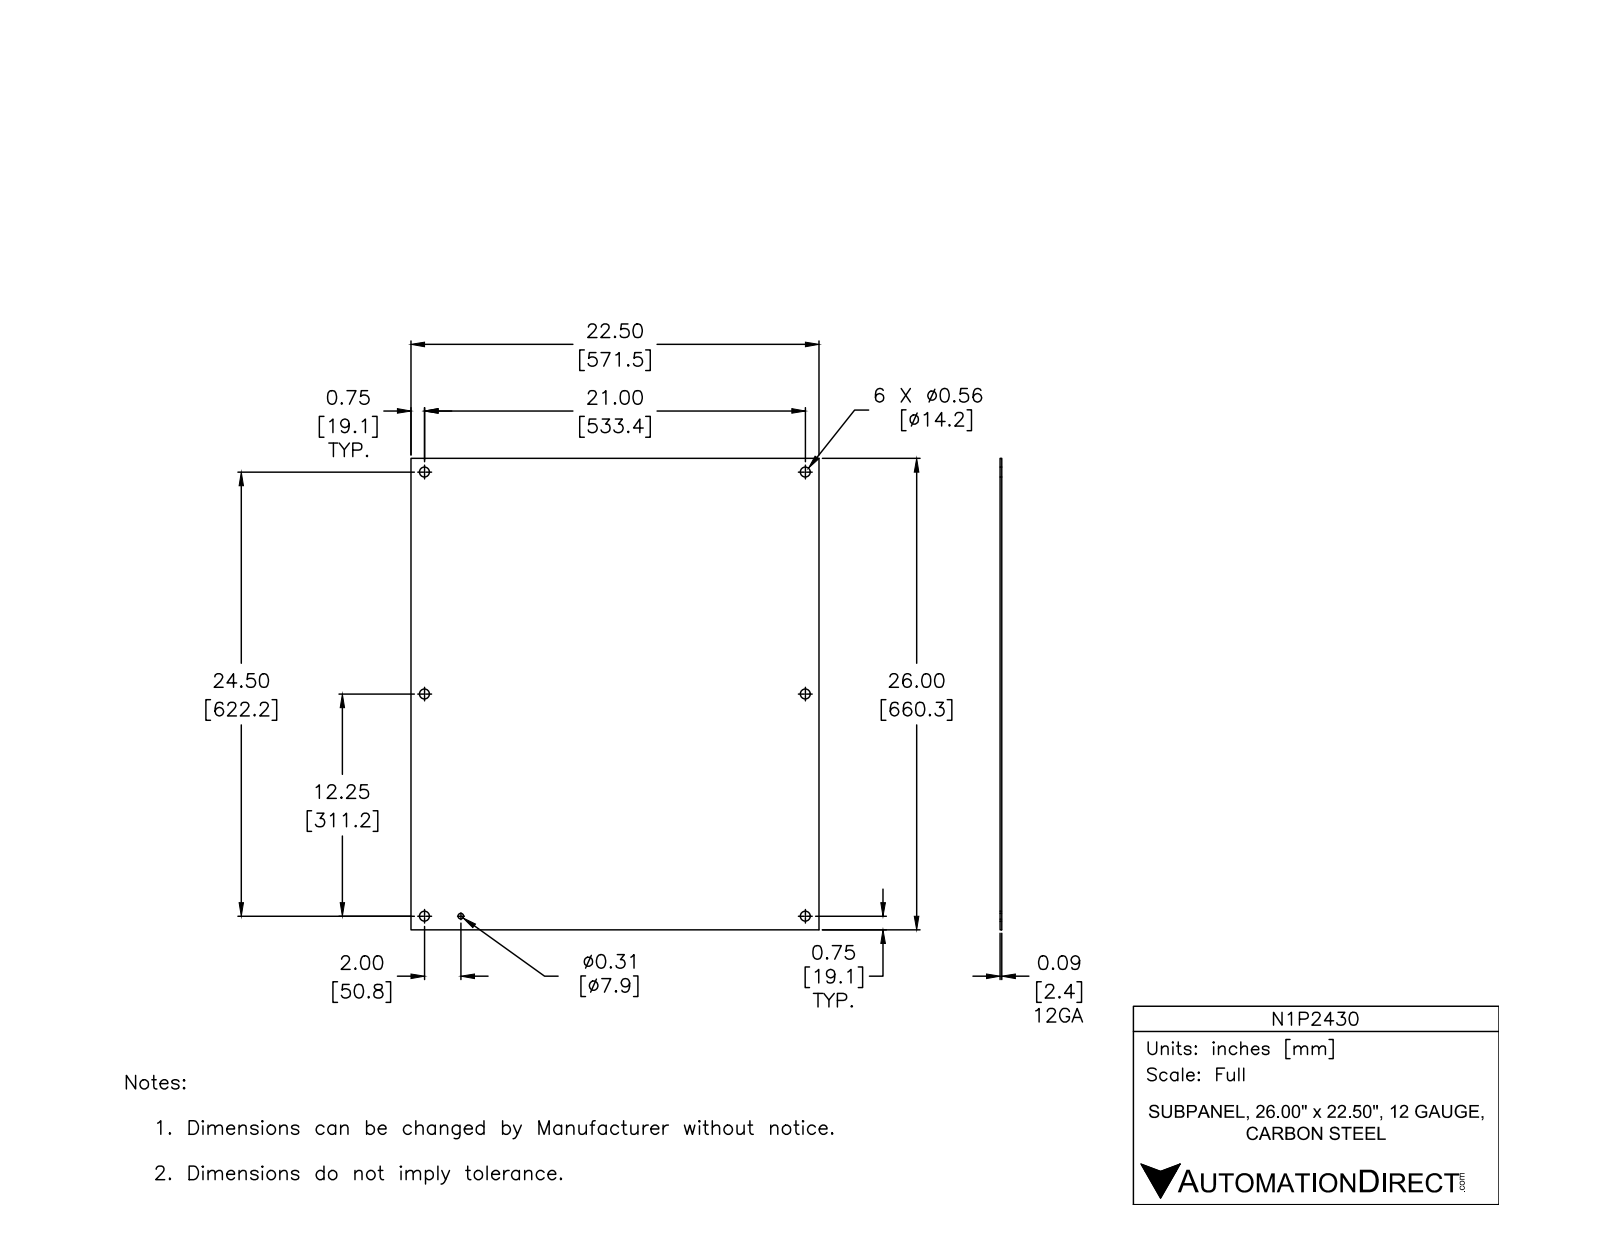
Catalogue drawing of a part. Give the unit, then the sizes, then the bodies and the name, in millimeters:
Units: millimetres
Overall size (bounding box): 660.4 × 571.5 × 2.4
Round holes (diameter × count): ⌀14.3 ×6, ⌀7.9 ×1
Main face-to-face distances: 2.4, 571.5, 660.4
Hole centre spacings: 311.2, 617.5, 533.4, 622.3, 819.6, 50.8, 315.3, 482.6
Volume: 896 400 mm³ · Surface area: 759 400 mm²
Bodies: 1 solid, 13 faces (6 planar, 7 cylindrical, 0 other)
Part name (STEP PRODUCT): N1P2430-1
STEP written by: Autodesk Inventor 2012 (AUTOMOTIVE_DESIGN)
